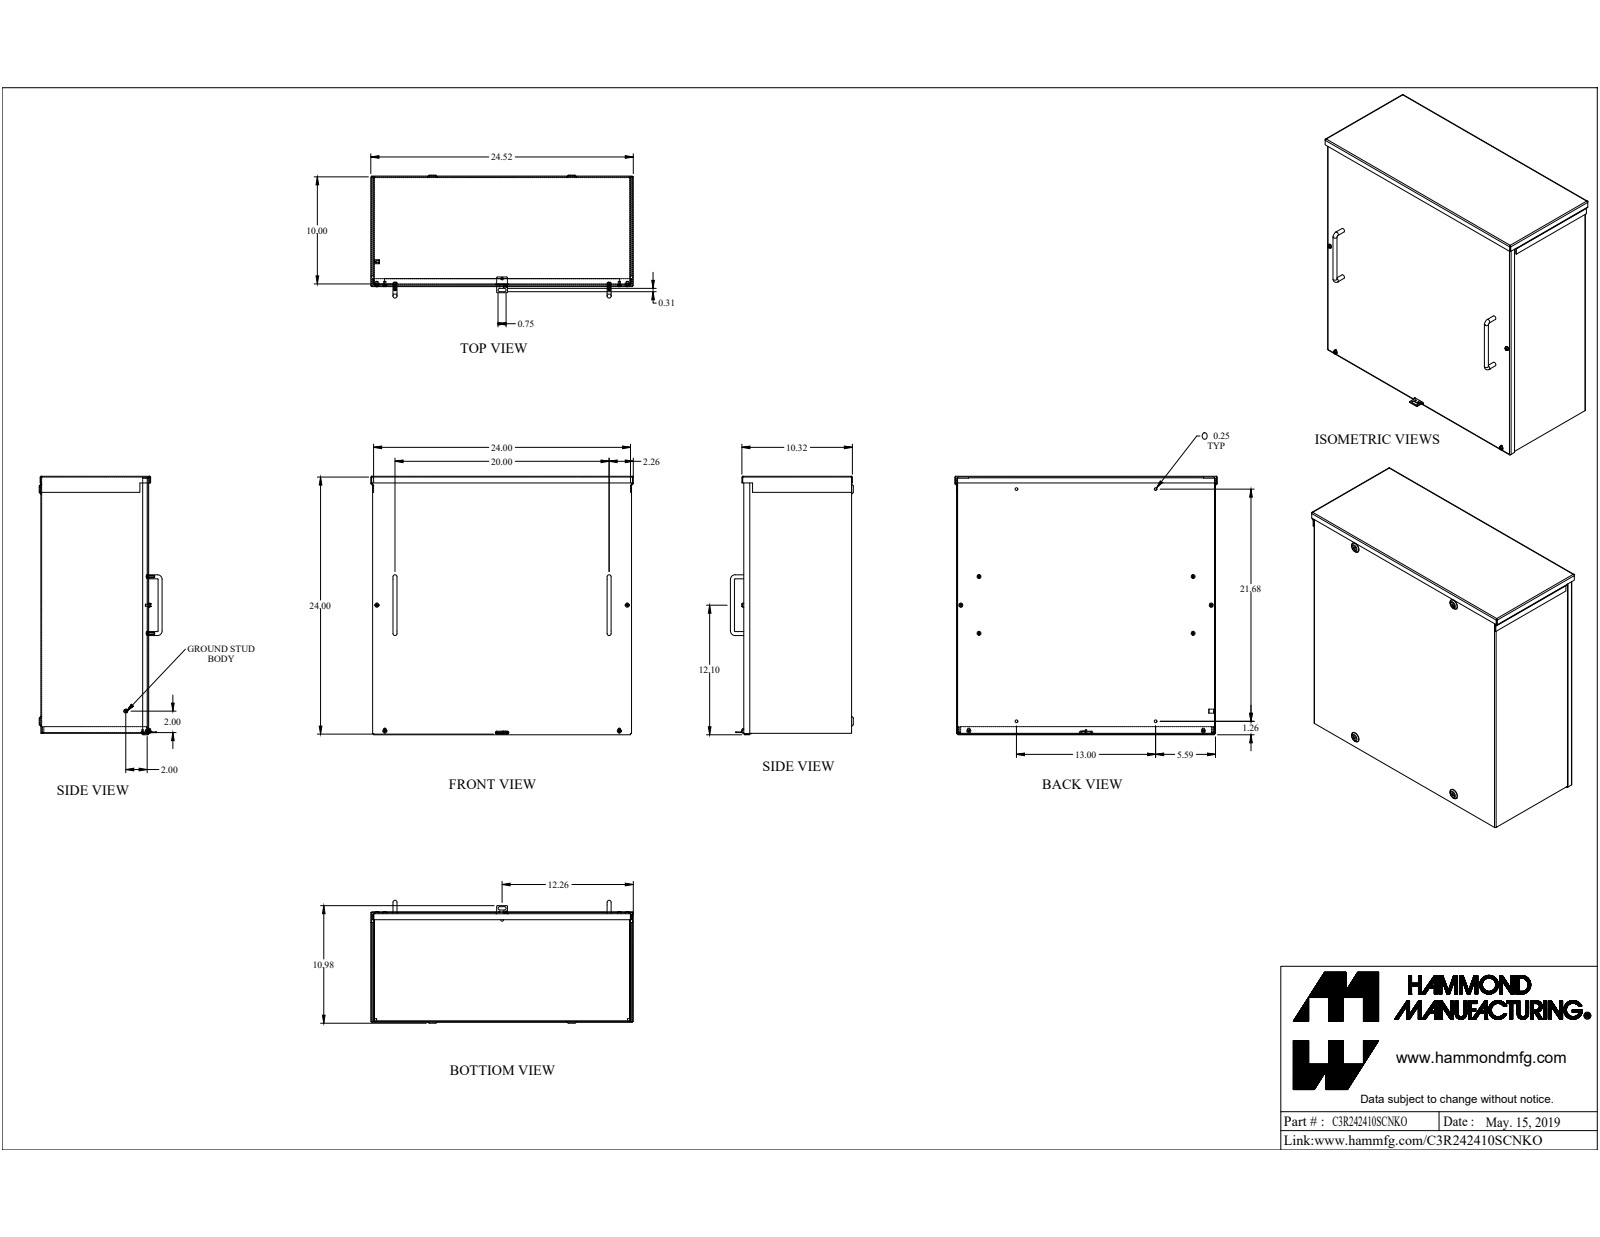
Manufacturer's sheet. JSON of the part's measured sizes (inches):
{"part_name": "C3R242410SCNKO", "step_written_by": "SolidWorks 2019 (AUTOMOTIVE_DESIGN)", "units": "inches", "bodies": {"solids": 17, "faces": 453, "planar": 287, "cylindrical": 106, "other": 60}, "overall_size": [24.519, 24.135, 11.478], "volume_in3": 162.6, "surface_area_in2": 4585, "round_holes": [[0.156, 5], [0.17, 4], [0.203, 4], [0.25, 4], [0.125, 1], [0.137, 1]], "round_bosses_or_shafts": [[0.375, 9], [0.19, 8], [0.367, 4], [0.375, 2], [0.125, 1]], "partial_cylinders_radius": [[0.036, 20], [0.108, 20], [0.109, 8], [0.125, 8], [0.156, 2], [0.029, 1], [0.086, 1]], "face_to_face_distances": [0.072, 10, 23.928, 9.928, 10.072, 24, 0.072, 23.856, 23.856, 23.928], "hole_center_spacings": [20, 0.024, 3.146, 5.3, 8.906, 12.02, 13.936, 18.42]}
